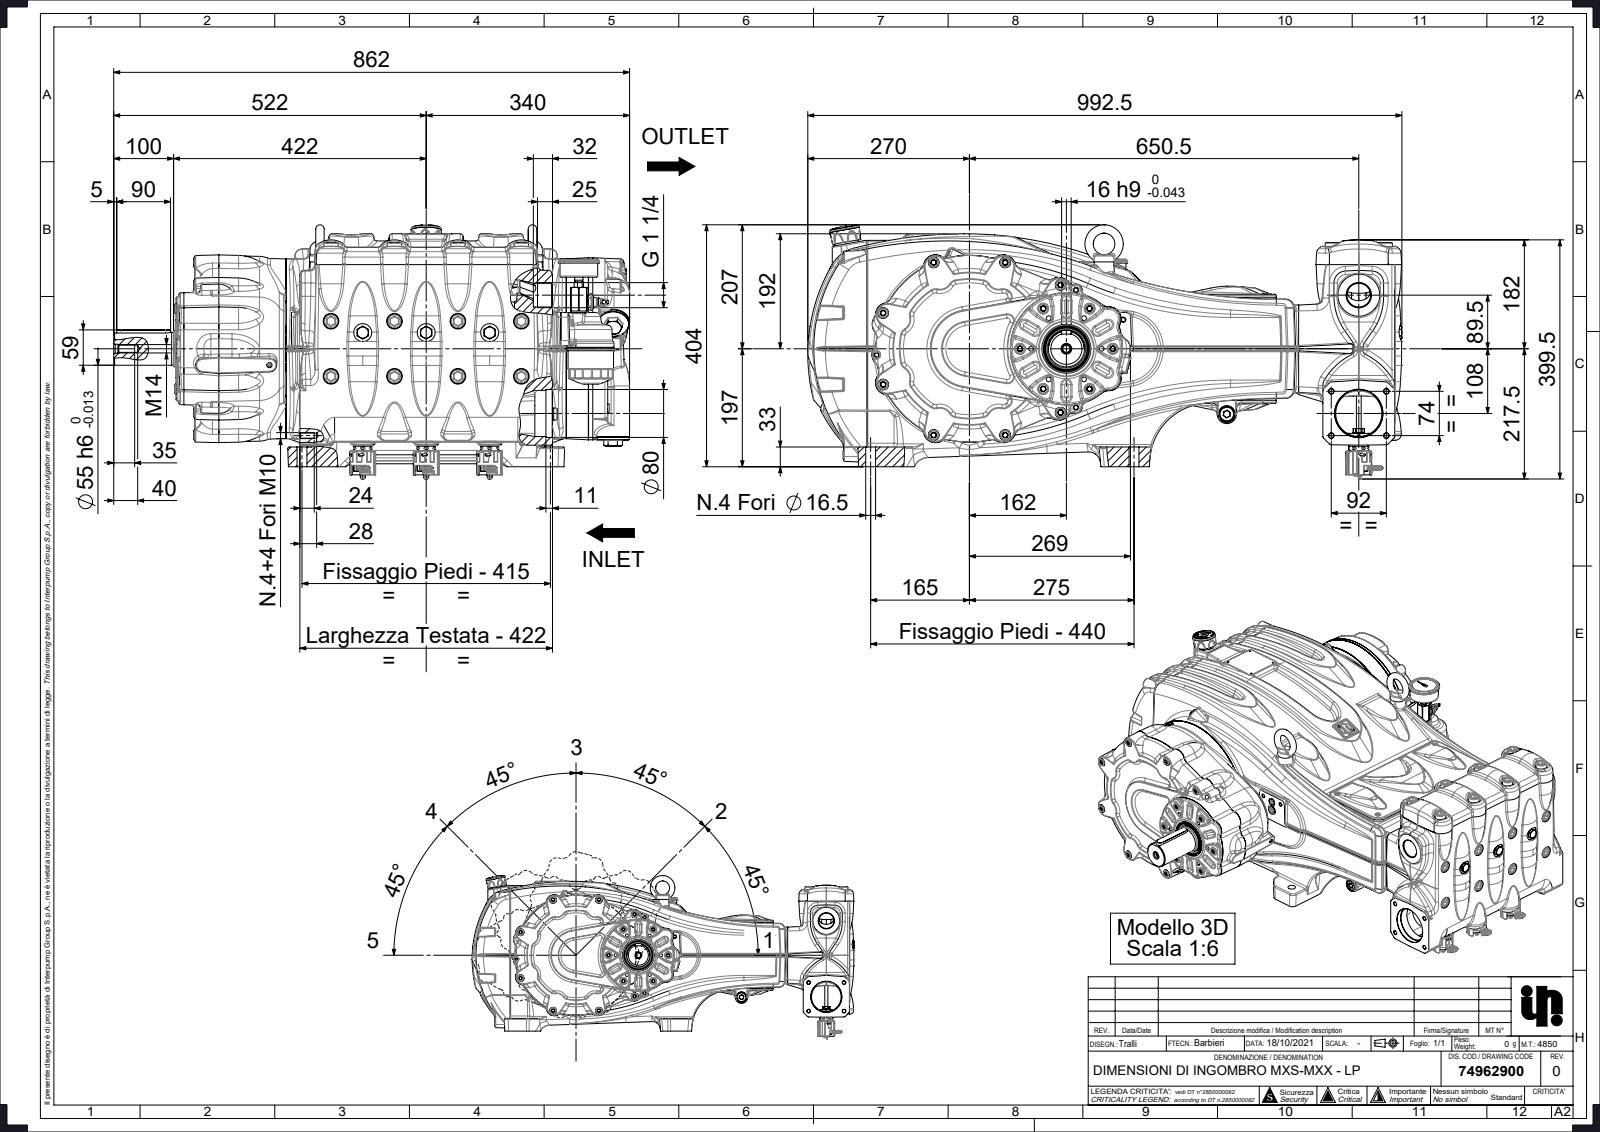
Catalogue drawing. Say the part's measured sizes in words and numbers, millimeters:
The part is named "9000630002-00020642; 1590069010-00014951; 9000309004-00019709; 1180396030-00013140 (+8 more)". Its 3-D file was written by "SolidWorks 2020 (AUTOMOTIVE_DESIGN)". It is 203 solids with 17623 faces: 2918 planar, 4182 cylindrical and 10523 other. Overall it measures 992.5 by 864.51 by 485.82 millimeters. Its volume is 131 900 000 cubic millimeters and its surface area 5 217 000 square millimeters. Round holes: 35 of diameter 14, 18 of diameter 9, 17 of diameter 17, 14 of diameter 8.5, 14 of diameter 13, 11 of diameter 5, 11 of diameter 20, 10 of diameter 16.5, 9 of diameter 25, 8 of diameter 8, 8 of diameter 12.3, 8 of diameter 13.5. Round bosses or shafts: 34 of diameter 16, 30 of diameter 8, 26 of diameter 13, 20 of diameter 10, 16 of diameter 24, 11 of diameter 12, 10 of diameter 18, 10 of diameter 6. Partial cylindrical surfaces (rounded edges, fillets, slot ends): 560 of radius 0.5, 156 of radius 0.3, 139 of radius 0.2, 114 of radius 2, 99 of radius 1.5, 92 of radius 5, 87 of radius 8, 73 of radius 1. The main face-to-face distances are 0.4, 468.4, 624.68, 7, 617.68, 617.3, 0.38, 7.38, 112.4, 504.9. The hole center spacings are 106, 246.38, 23, 110.31, 190.88, 103, 212, 46.
